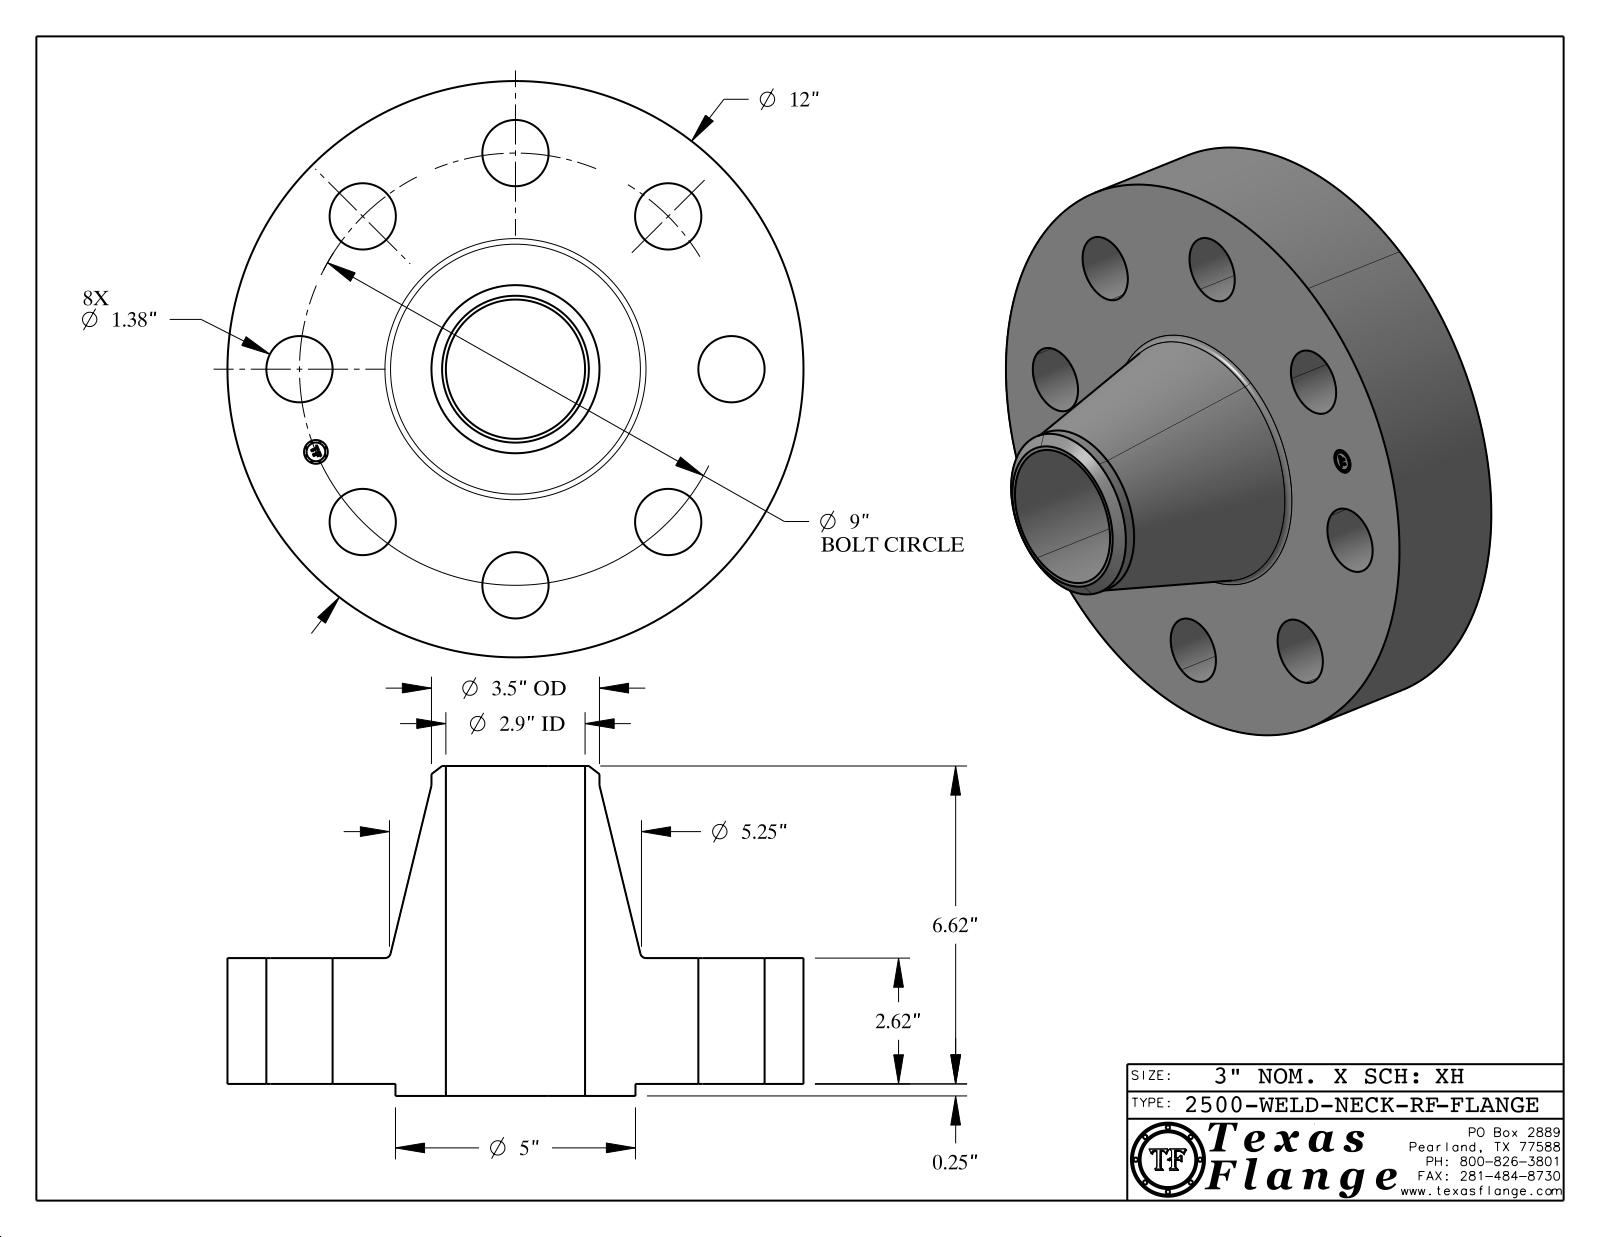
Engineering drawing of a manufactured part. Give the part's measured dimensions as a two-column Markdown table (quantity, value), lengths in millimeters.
| quantity | value |
| --- | --- |
| part name | 2500-WELD-NECK-RF |
| STEP written by | CATIA V5 STEP AP214 (AUTOMOTIVE_DESIGN) |
| units | millimeters |
| bodies | 1 solid, 419 faces (369 planar, 44 cylindrical, 6 other) |
| overall size | 304.8 × 304.8 × 174.5 |
| volume | 4 638 000 mm³ |
| surface area | 314 100 mm² |
| round holes (diameter × count) | 35.1 × 8, 12.6 × 1, 73.7 × 1 |
| round bosses / shafts (diameter × count) | 0.8 × 8, 304.8 × 1, 127 × 1, 88.9 × 1, 9.9 × 1 |
| main face-to-face distances | 66.5, 6.4, 72.9, 174.5, 168.1, 101.6, 72.5, 66.2, 0.4, 102 |
| hole center spacings | 114.3, 87.5, 161.6, 211.2, 44.6, 127, 190.1, 228.6 |
